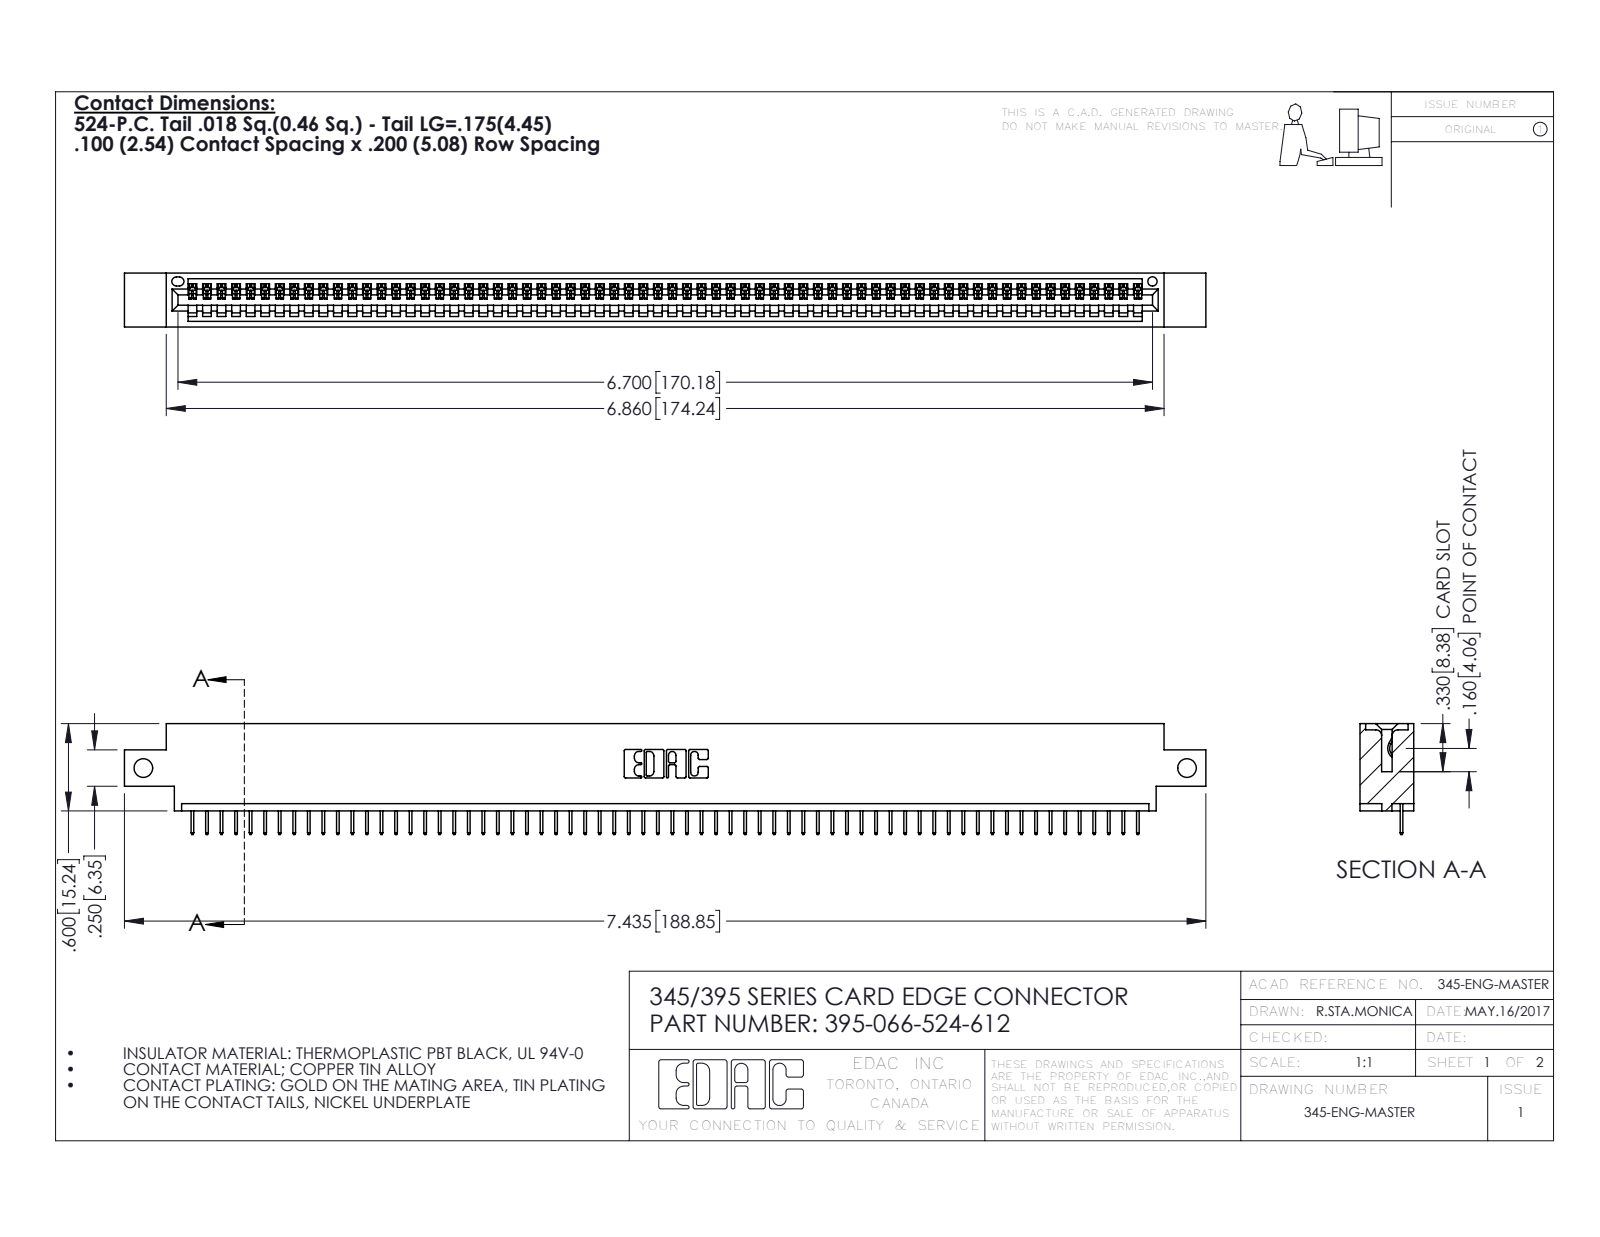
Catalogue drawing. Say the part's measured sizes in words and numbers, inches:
The part is named "345 Part_0.170 Offset - Side Mount; 345-292-001_345-293-124; 395-066-524-612". Its 3-D file was written by "SolidWorks 2016 (CONFIG_CONTROL_DESIGN)". It is 67 solids with 4222 faces: 3120 planar, 1102 cylindrical and 0 other. Overall it measures 7.435 by 0.762 by 0.37 inches. Its volume is 1.078 cubic inches and its surface area 35.59 square inches. Round holes: 2 of diameter 0.128, 1 of diameter 0.064. Partial cylindrical surfaces (rounded edges, fillets, slot ends): 132 of radius 0.006, 22 of radius 0.01, 6 of radius 0.007, 6 of radius 0.031, 3 of radius 0.026, 2 of radius 0.031, 2 of radius 0.04, 1 of radius 0.014. The main face-to-face distances are 0.072, 0.298, 0.37, 0.2, 0.098, 0.272, 0.025, 0.225, 0.072, 0.175. The hole center spacings are 7.175.
